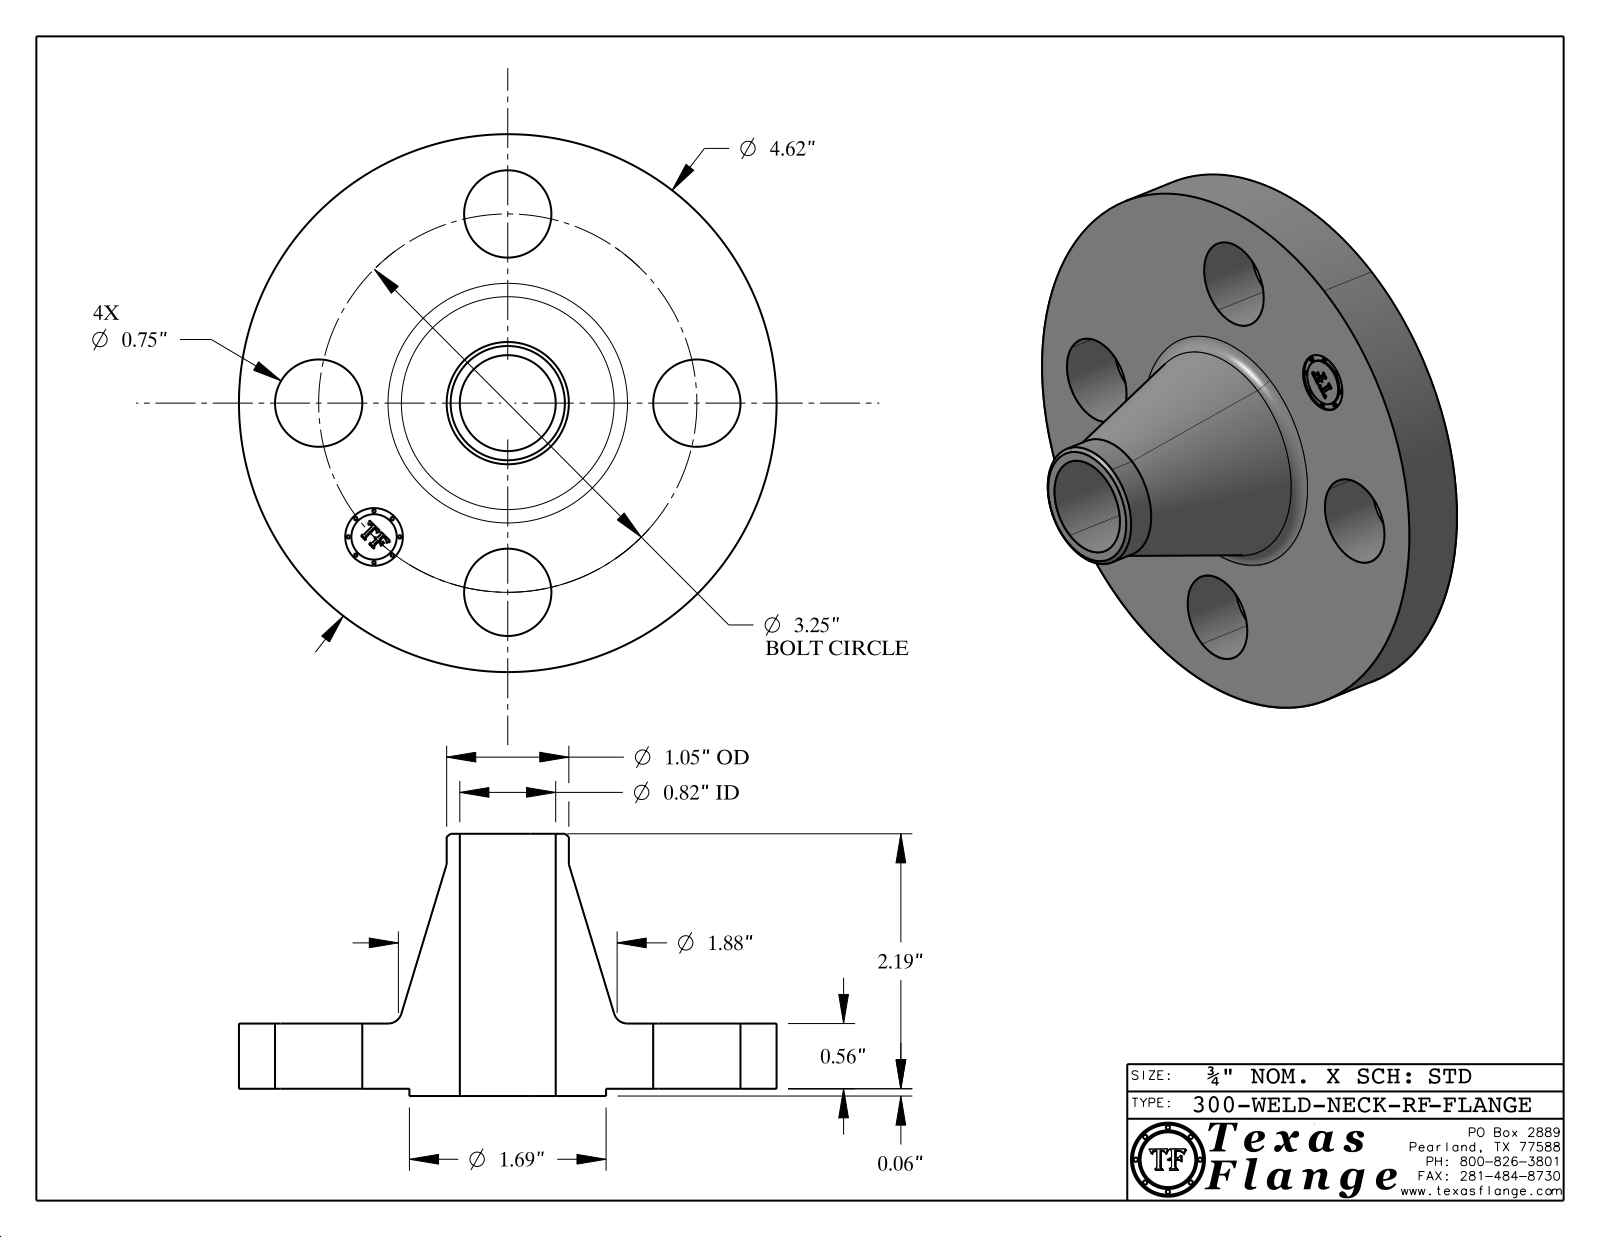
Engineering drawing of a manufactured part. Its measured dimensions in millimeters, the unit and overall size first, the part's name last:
Units: millimetres
Overall size (bounding box): 117.3 × 117.3 × 57.2
Round holes (diameter × count): ⌀19.1 ×4, ⌀12.6 ×1, ⌀20.9 ×1
Round bosses / shafts (diameter × count): ⌀0.8 ×8, ⌀117.3 ×1, ⌀42.9 ×1, ⌀26.7 ×1, ⌀9.9 ×1
Main face-to-face distances: 14.2, 1.6, 15.8, 57.2, 55.6, 41.4, 15.4, 13.8, 0.4, 41.8
Hole centre spacings: 41.3, 58.4, 31.6, 76.3, 82.6
Volume: 162 900 mm³ · Surface area: 34 790 mm²
Bodies: 1 solid, 411 faces (369 planar, 36 cylindrical, 6 other)
Part name (STEP PRODUCT): 300-WELD-NECK-RF
STEP written by: CATIA V5 STEP AP214 (AUTOMOTIVE_DESIGN)
